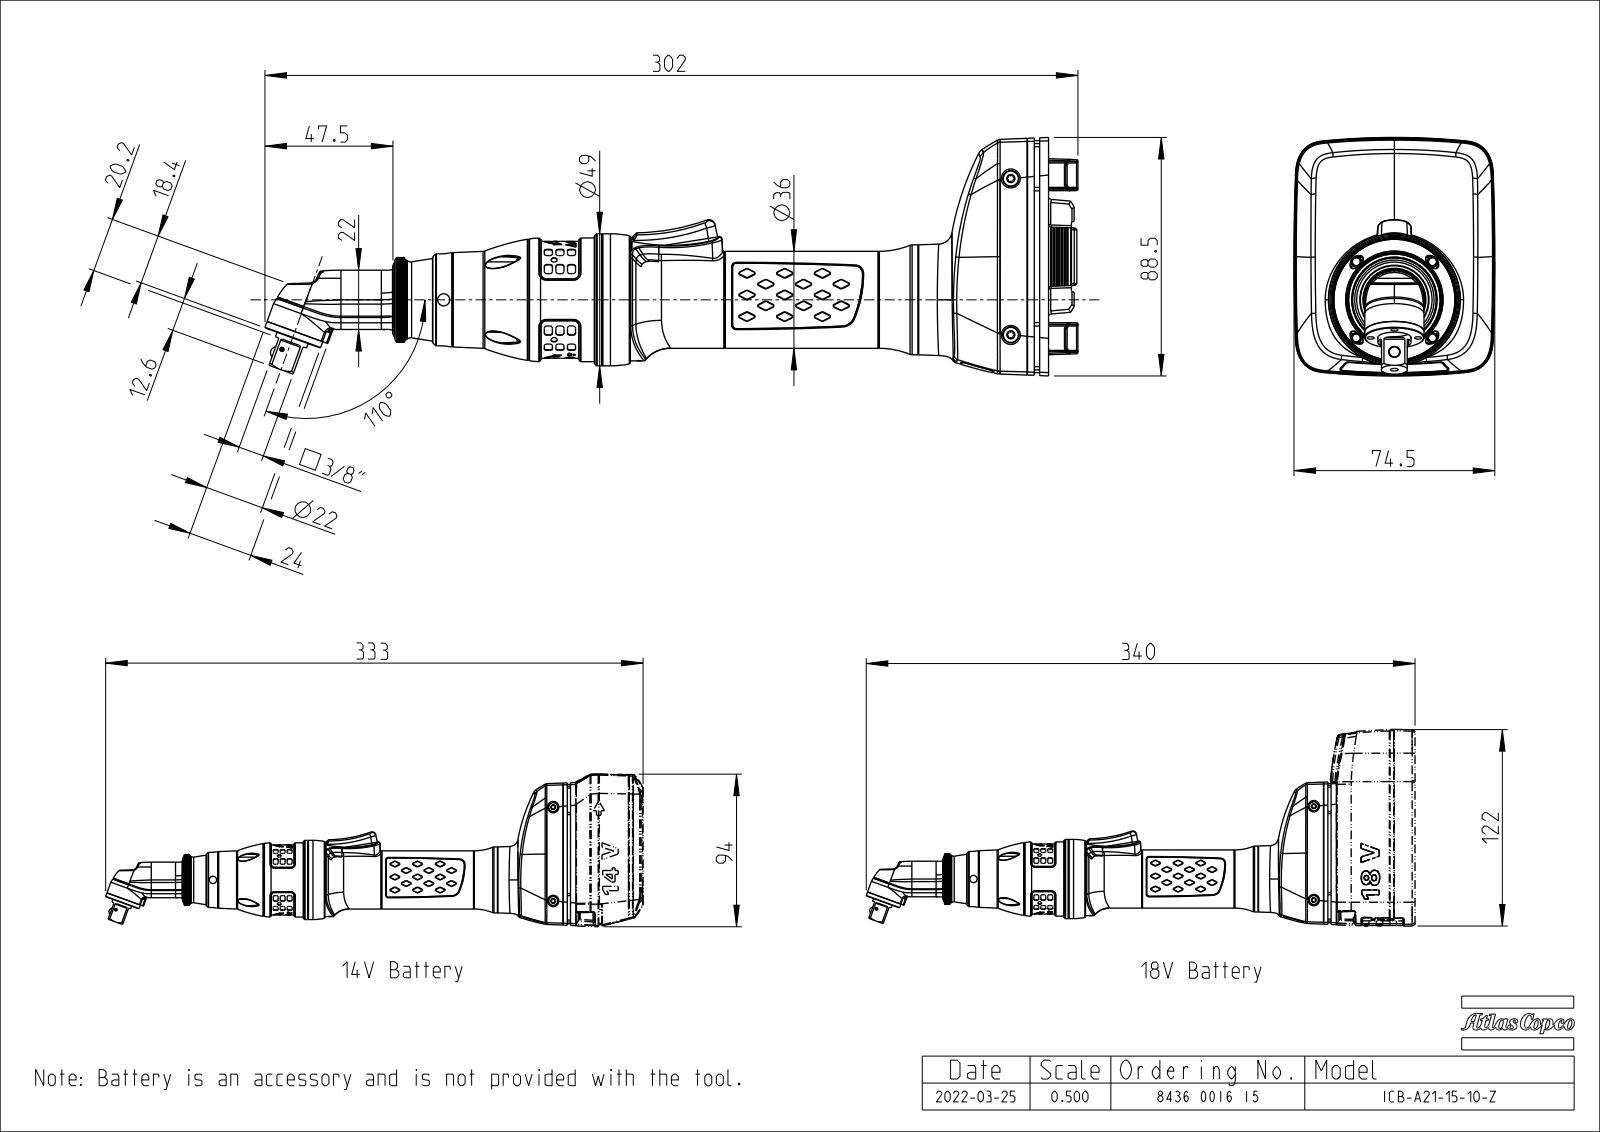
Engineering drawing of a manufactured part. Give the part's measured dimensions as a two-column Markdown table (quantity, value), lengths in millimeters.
| quantity | value |
| --- | --- |
| part name | EXT_COMP_SW0005 |
| STEP written by | CREO PARAMETRIC BY PTC INC, 2020281 (CONFIG_CONTROL_DESIGN) |
| units | millimeters |
| bodies | 2 solids, 10161 faces (6729 planar, 1048 cylindrical, 2384 other) |
| overall size | 301.8 × 88.5 × 74.5 |
| volume | 463 900 mm³ |
| surface area | 75 940 mm² |
| round holes (diameter × count) | 2.6 × 4, 4.5 × 2, 6 × 2, 1.2 × 1, 1.5 × 1, 3.5 × 1, 3.9 × 1, 12.5 × 1, 14.4 × 1, 42.8 × 1, 43.7 × 1, 46.2 × 1 |
| round bosses / shafts (diameter × count) | 8 × 4, 5.6 × 3, 49 × 1, 45.9 × 1, 45.3 × 1, 43.5 × 1, 43.4 × 1, 42.9 × 1 |
| partial cylindrical surfaces (radius × count) | 0.5 × 84, 1 × 77, 0.2 × 34, 0.2 × 31, 0.3 × 30, 0.5 × 30, 0.3 × 24, 0.4 × 24 |
| main face-to-face distances | 120.5, 120.5, 10.5, 131, 131, 8.4, 60, 10.7, 120.3, 120.3 |
| hole center spacings | 8.8, 12.4, 17.6, 58, 62.8, 210.9, 215.3, 230.6 |
